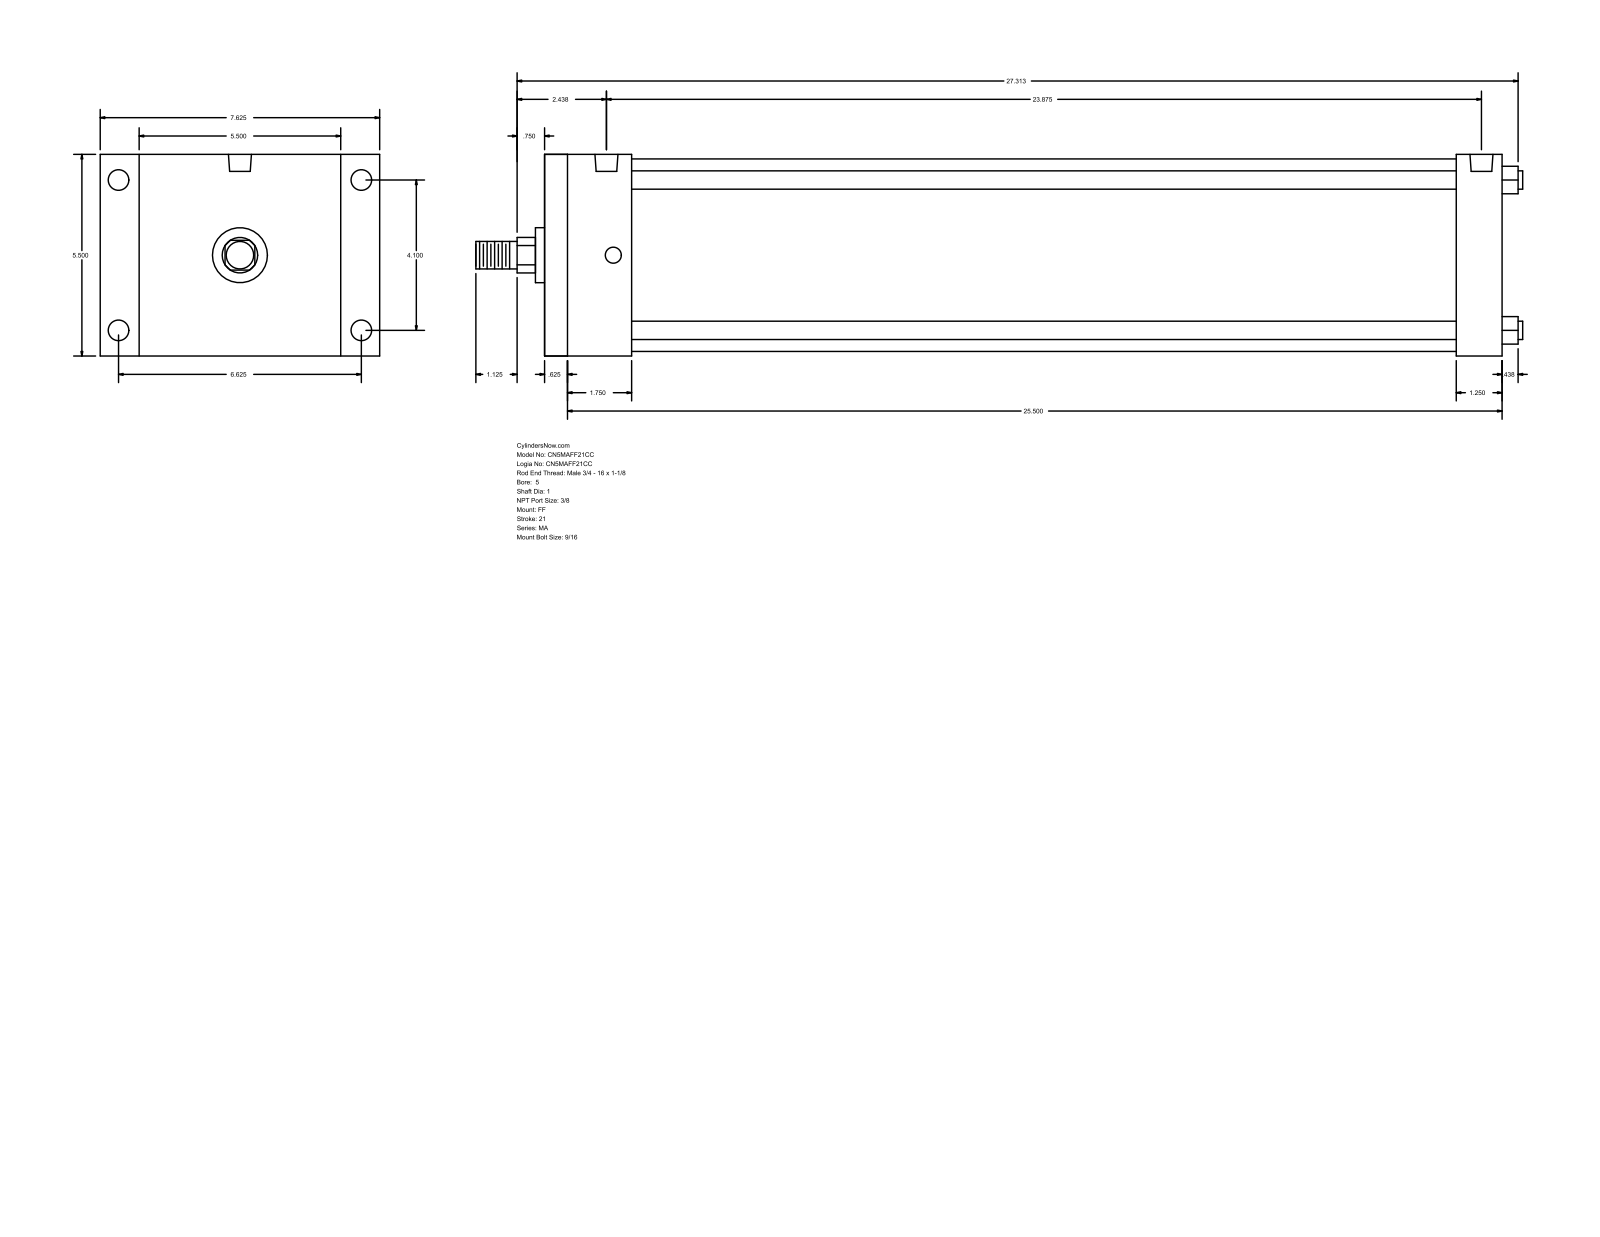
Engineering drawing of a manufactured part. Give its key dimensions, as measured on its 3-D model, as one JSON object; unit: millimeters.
{"part_name": "MA_FF__0500_1", "step_written_by": "GSSL Pune (CONFIG_CONTROL_DESIGN)", "units": "millimeters", "bodies": {"solids": 0, "faces": 92, "planar": 64, "cylindrical": 28, "other": 0}, "overall_size": [725.49, 193.68, 139.7], "round_holes": [[11.11, 4], [14.29, 4], [15.93, 2]], "round_bosses_or_shafts": [[12.7, 4], [133.35, 1], [38.1, 1], [25.4, 1], [19.05, 1]], "partial_cylinders_radius": [[12.29, 1]], "face_to_face_distances": [139.7, 663.57, 15.87, 647.7, 631.83, 615.96, 31.74, 60.33, 44.46, 571.5], "hole_center_spacings": [4.76, 104.14, 168.28, 197.9, 596.91, 601.67, 606.43]}
